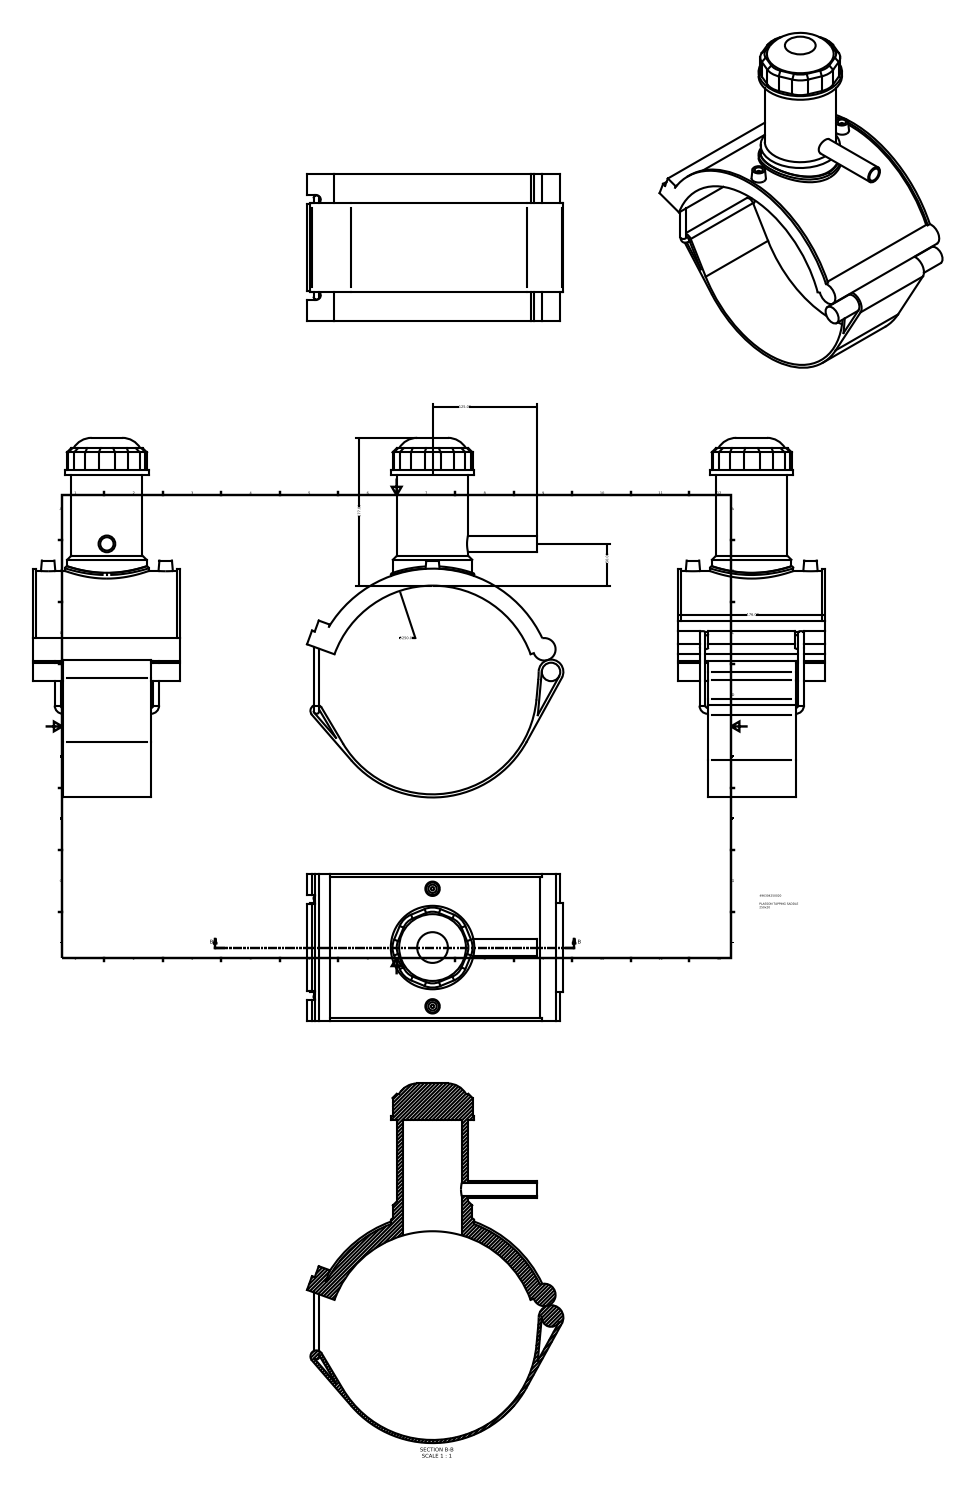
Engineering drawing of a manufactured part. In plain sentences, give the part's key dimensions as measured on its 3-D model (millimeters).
The part is named "496304250020". Its 3-D file was written by "Autodesk Inventor 2015 (AUTOMOTIVE_DESIGN)". It is 1 solid with 121 faces: 68 planar, 38 cylindrical and 15 other. Overall it measures 430.75 by 307.08 by 176 millimeters. Its volume is 1 941 000 cubic millimeters and its surface area 374 768 square millimeters. Round holes: 2 of diameter 10, 1 of diameter 16, 1 of diameter 70. Round bosses or shafts: 2 of diameter 7, 2 of diameter 4, 1 of diameter 100, 1 of diameter 95, 1 of diameter 85, 1 of diameter 22.12, 1 of diameter 20. Partial cylindrical surfaces (rounded edges, fillets, slot ends): 8 of radius 25, 2 of radius 5.25, 2 of radius 125, 1 of radius 3.5, 1 of radius 7.25, 1 of radius 13.46, 1 of radius 14.81, 1 of radius 128.75. The main face-to-face distances are 3.75, 176, 3.78, 35.2, 140.8, 17.5, 14, 3.34, 31.51, 3.5. The hole center spacings are 70.4, 140.8.
